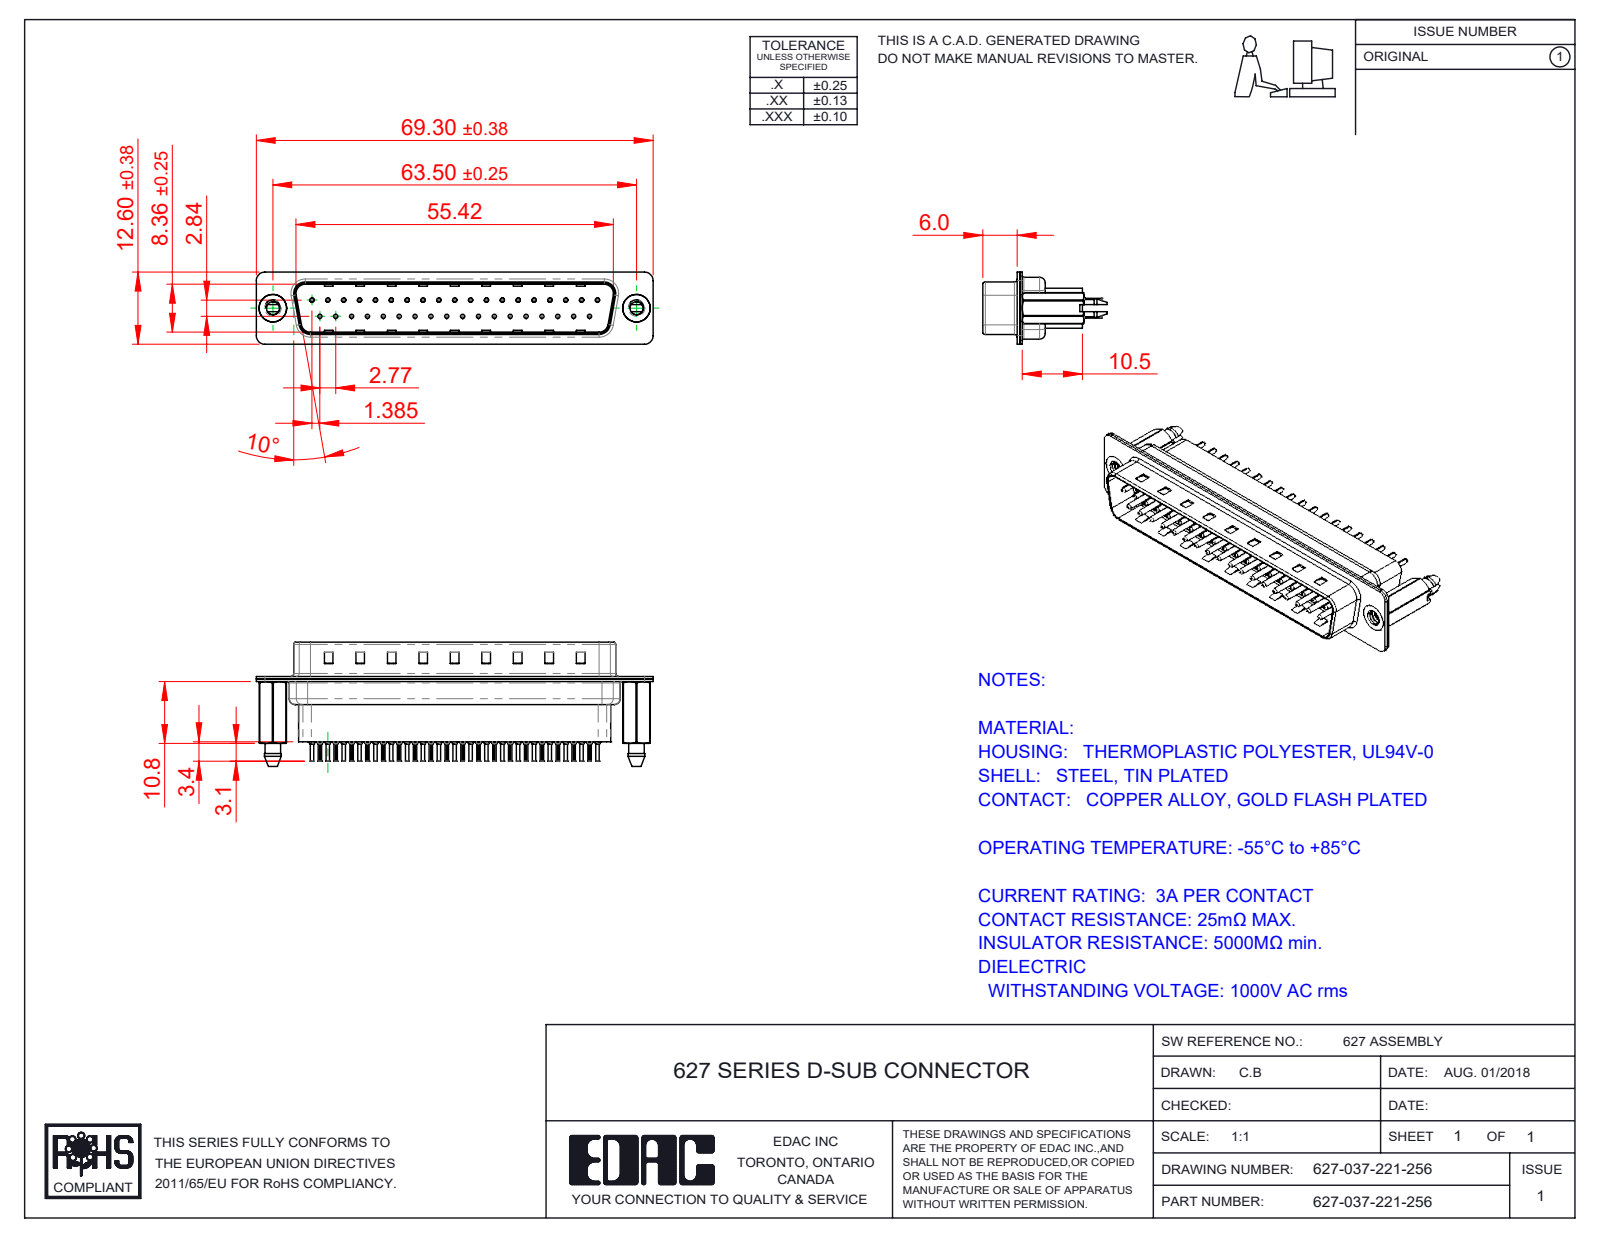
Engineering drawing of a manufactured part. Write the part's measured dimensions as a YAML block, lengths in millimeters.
part_name: "627 Contact Row 2_21H; 627 Contact Row 1_21H; 627 Shell Rear_37 Contacts; 627-037-221-056 (+3 more)"
step_written_by: "SolidWorks 2020 (CONFIG_CONTROL_DESIGN)"
units: millimeters
bodies: {solids: 42, faces: 4152, planar: 1123, cylindrical: 1578, other: 1451}
overall_size: [69.3, 21.7, 12.6]
volume: 5558
surface_area: 14141
round_holes:
  - {diameter: 0.2, count: 37}
  - {diameter: 0.35, count: 37}
  - {diameter: 1.1, count: 37}
  - {diameter: 1.6, count: 37}
  - {diameter: 2.26, count: 2}
  - {diameter: 4, count: 2}
  - {diameter: 4.8, count: 2}
round_bosses_or_shafts:
  - {diameter: 2, count: 37}
  - {diameter: 1.5, count: 37}
  - {diameter: 0.75, count: 37}
  - {diameter: 0.6, count: 37}
  - {diameter: 4.9, count: 2}
partial_cylinders:
  - {radius: 0.1, count: 74}
  - {radius: 1.5, count: 18}
  - {radius: 2, count: 12}
  - {radius: 1.6, count: 10}
  - {radius: 0.5, count: 8}
  - {radius: 0.25, count: 4}
  - {radius: 0.6, count: 4}
  - {radius: 0.65, count: 4}
face_to_face_distances: [0.4, 0.82, 9.58, 0.45, 0.68, 7.68, 1.5, 1.08, 8.08, 8.76]
hole_center_spacings: [3.16, 2.77, 5.54, 8.31, 5.04, 10.1, 11.08, 12.78]
